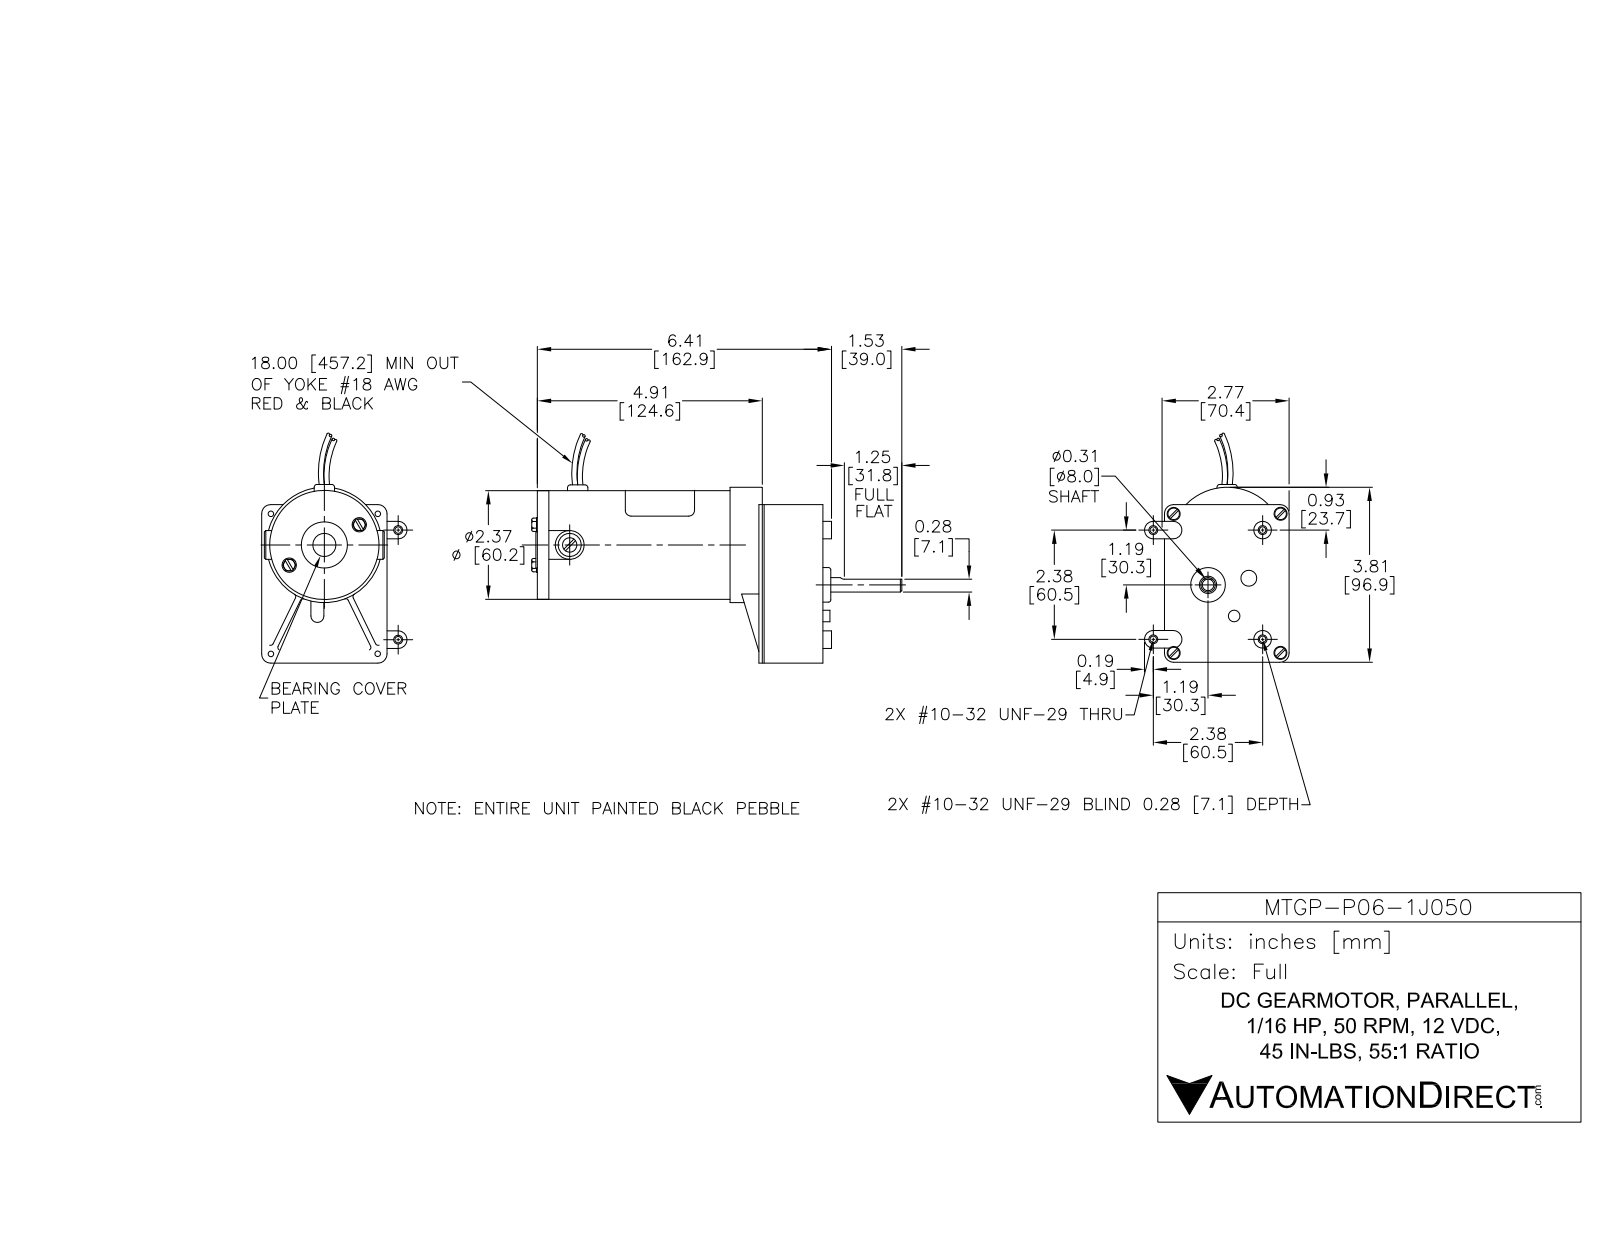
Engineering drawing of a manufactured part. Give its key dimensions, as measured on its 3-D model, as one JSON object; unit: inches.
{"part_name": "MTGP-P06-1J050", "step_written_by": "SolidWorks 2016 (AUTOMOTIVE_DESIGN)", "units": "inches", "bodies": {"solids": 27, "faces": 266, "planar": 115, "cylindrical": 130, "other": 21}, "overall_size": [7.922, 5.092, 3.181], "volume_in3": 20.18, "surface_area_in2": 156.4, "round_holes": [[0.194, 5], [0.063, 4], [0.283, 4], [0.156, 2], [0.25, 1], [0.312, 1], [0.562, 1], [1, 1], [2.25, 1]], "round_bosses_or_shafts": [[0.312, 4], [0.38, 2], [0.1, 2], [2.46, 1], [2.375, 1], [0.75, 1], [0.625, 1], [0.625, 1]], "partial_cylinders_radius": [[0.031, 10], [0.1, 4], [0.19, 4], [0.25, 2], [0.134, 1], [0.141, 1], [1.222, 1]], "face_to_face_distances": [1.4, 0.25, 4.833, 6.233, 4.583, 5.983, 4.194, 3.944, 0.639, 2.039], "hole_center_spacings": [1.223, 1.729, 0.373, 0.44, 0.875, 1.306, 1.332, 1.539]}
